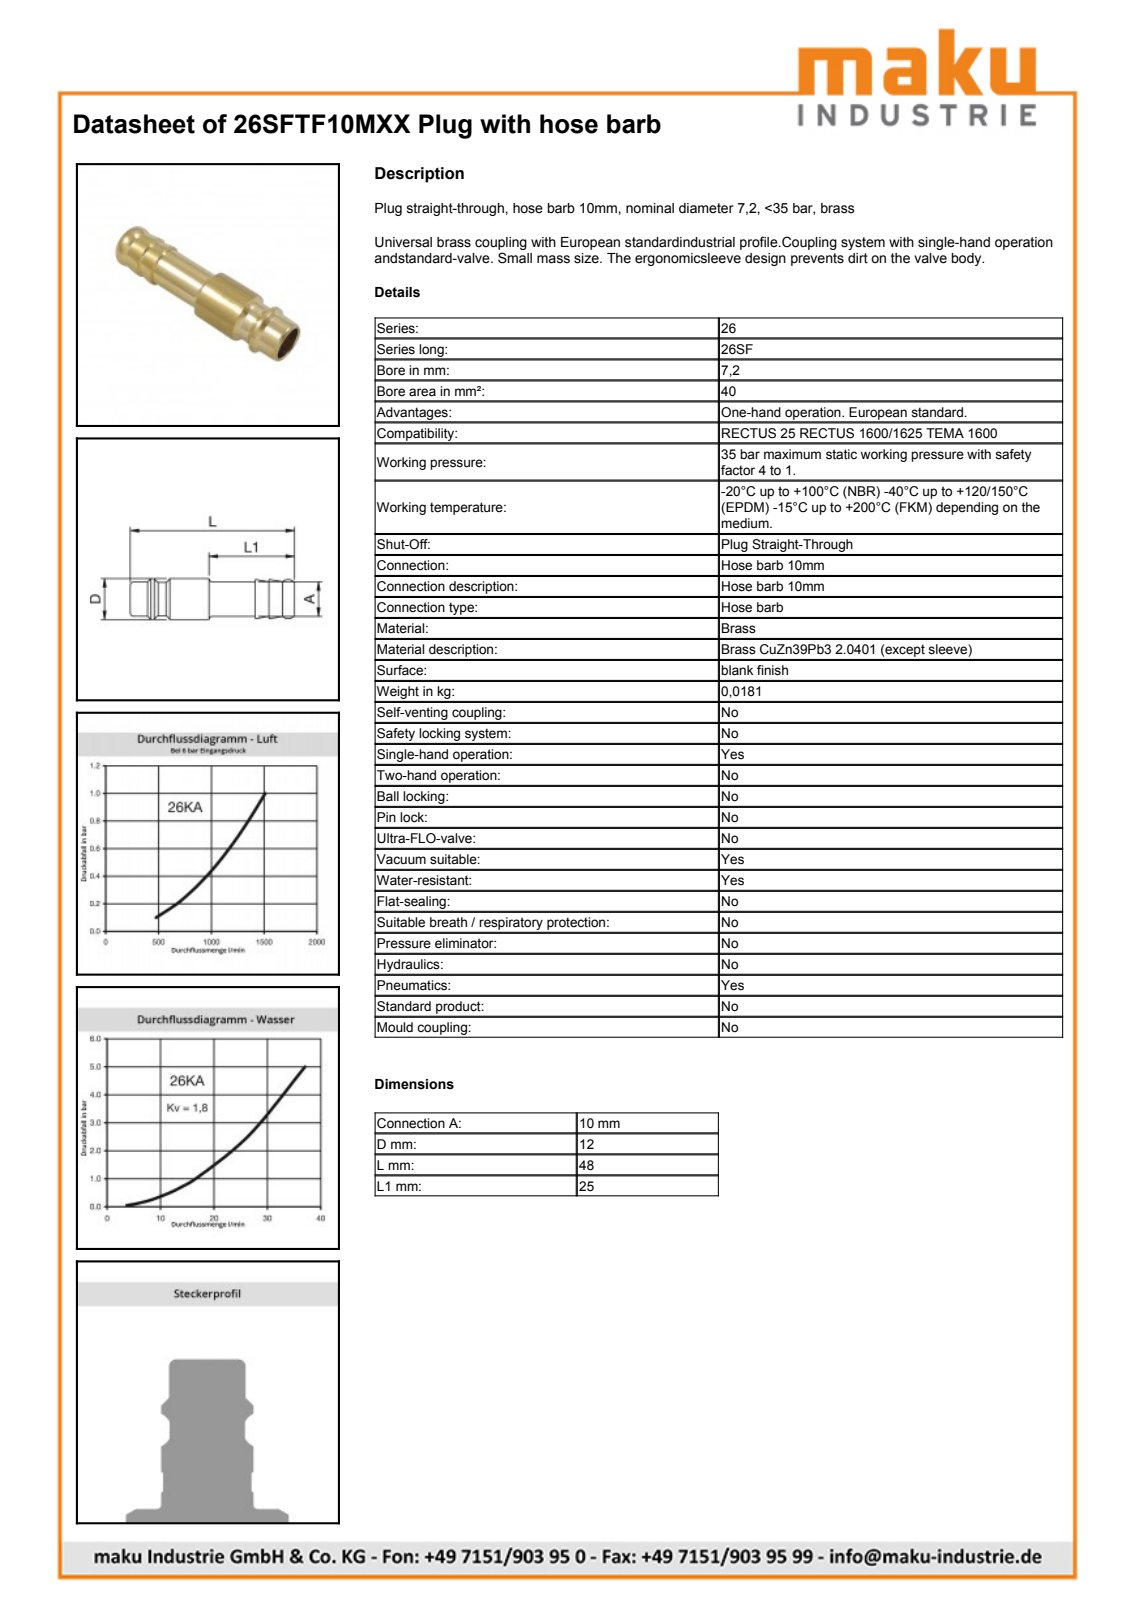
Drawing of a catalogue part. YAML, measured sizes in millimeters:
part_name: "D106813"
step_written_by: "Autodesk Inventor 2013 (AUTOMOTIVE_DESIGN)"
units: millimeters
bodies: {solids: 1, faces: 20, planar: 3, cylindrical: 6, other: 11}
overall_size: [48, 12, 12]
volume: 2098
surface_area: 2967
round_holes:
  - {diameter: 7.85, count: 1}
round_bosses_or_shafts:
  - {diameter: 12, count: 1}
  - {diameter: 10.1, count: 1}
  - {diameter: 10, count: 1}
  - {diameter: 9.75, count: 1}
face_to_face_distances: [11.5, 36.5, 48]
